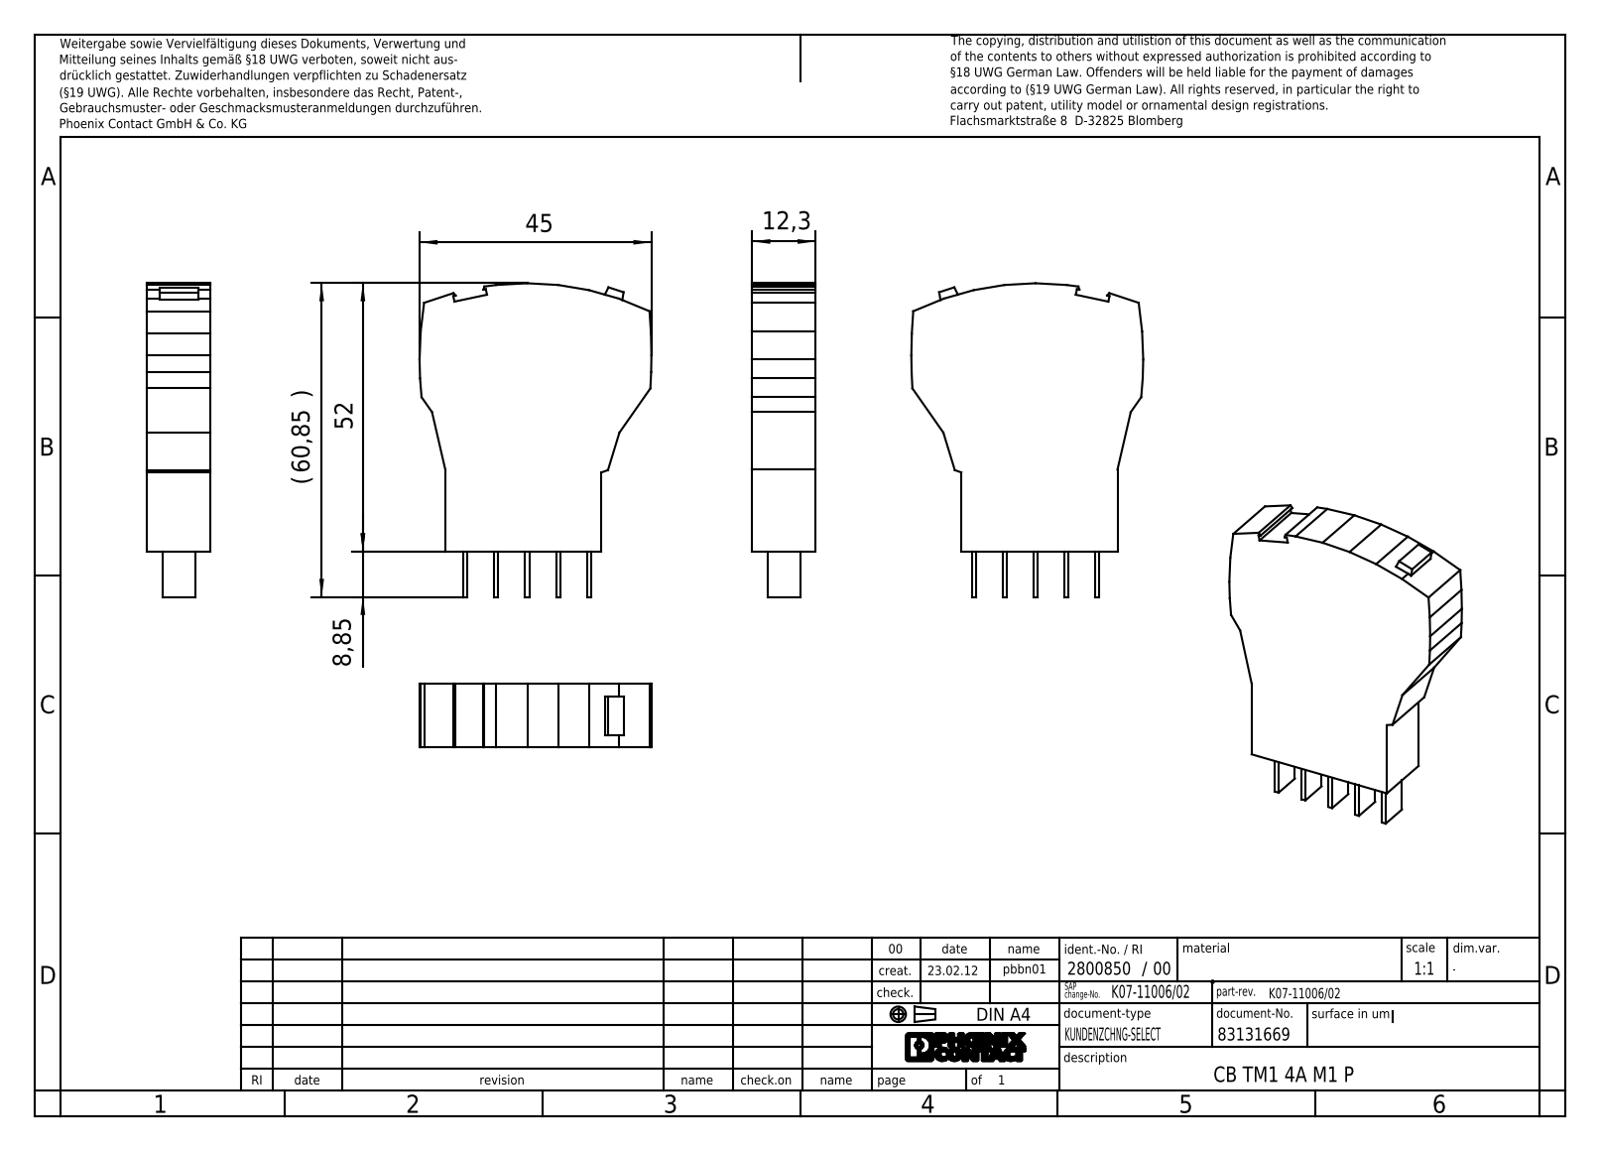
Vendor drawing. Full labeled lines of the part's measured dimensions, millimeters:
Part name (STEP PRODUCT): CB_TM1_4A_M1_P-select
STEP written by: Creo Elements/Direct Modeling 20.1A 29-Sep-2018 (C) Parametric Technology GmbH (AUTOMOTIVE_DESIGN)
Units: millimetres
Bodies: 1 solid, 62 faces (62 planar, 0 cylindrical, 0 other)
Overall size (bounding box): 60.85 × 45 × 12.3
Volume: 23 513 mm³ · Surface area: 6 640 mm²
Main face-to-face distances: 12.3, 6, 12, 0.8, 6.8, 18, 5.2, 30.3, 12.8, 11.2
